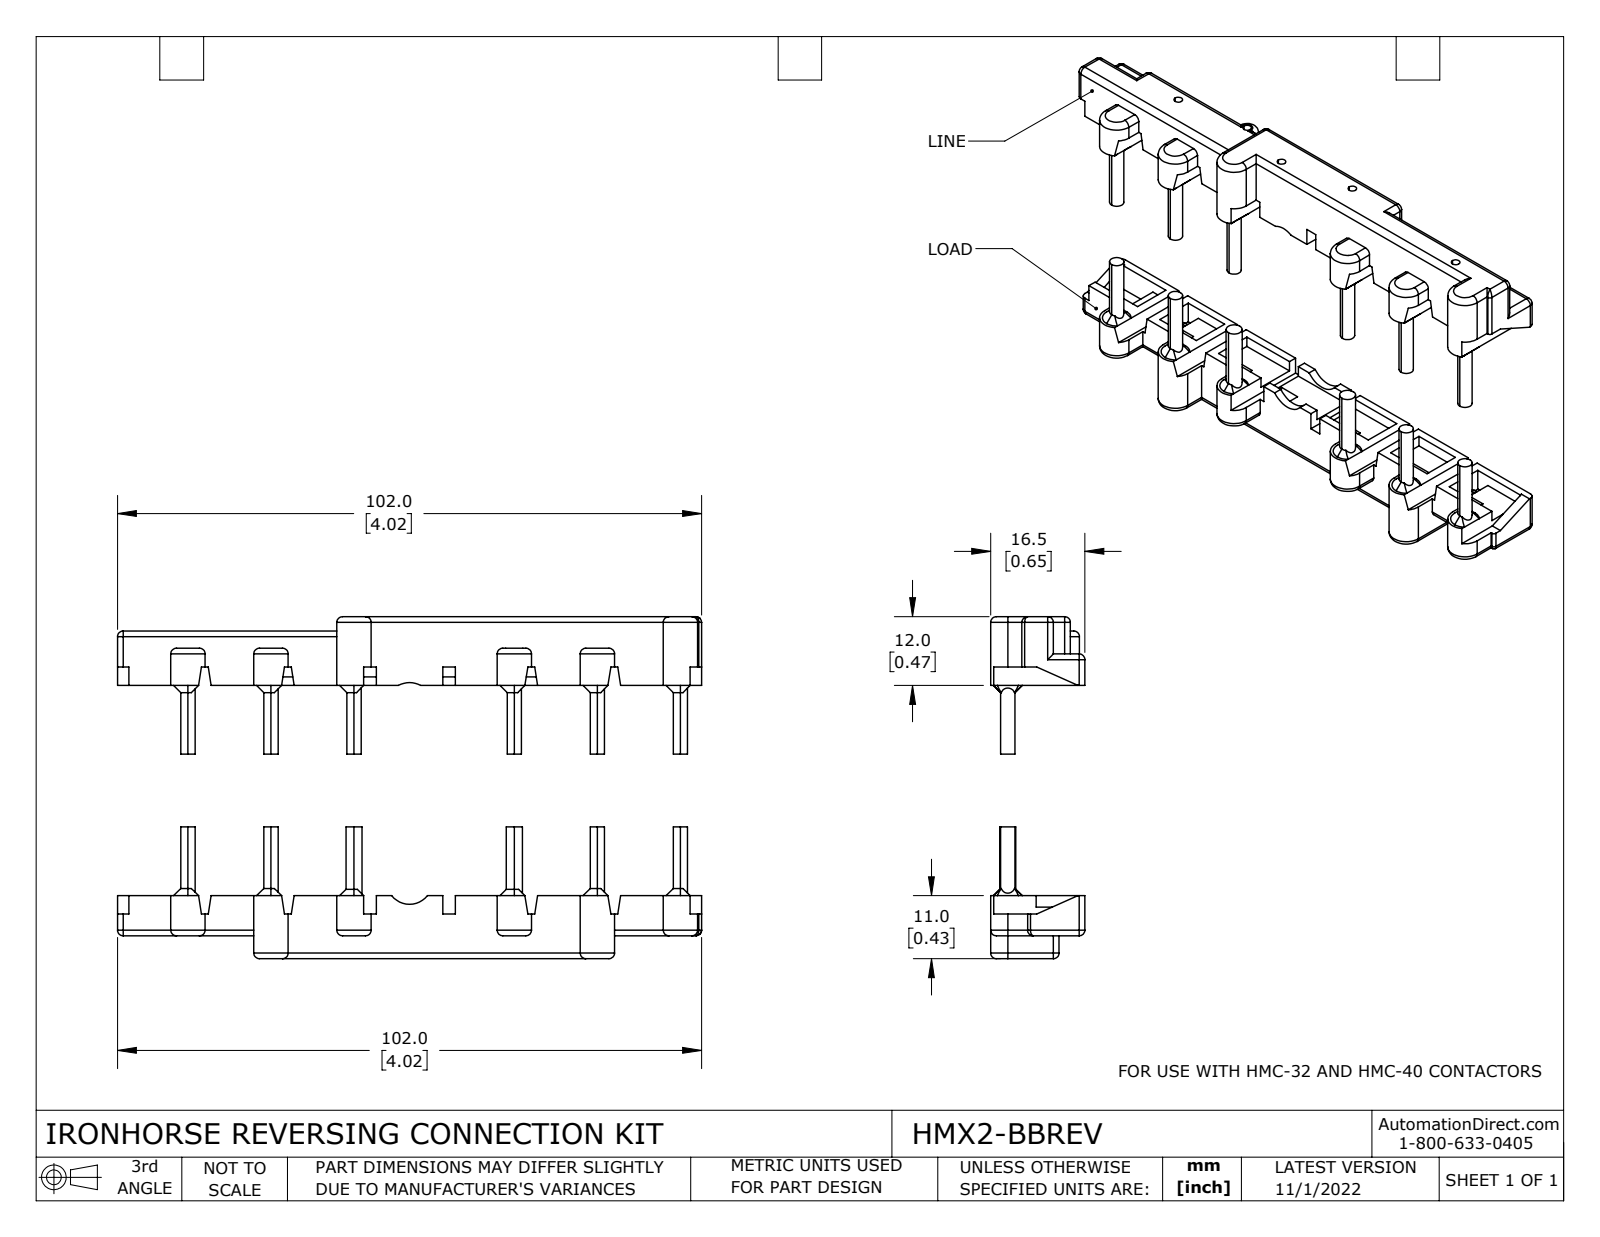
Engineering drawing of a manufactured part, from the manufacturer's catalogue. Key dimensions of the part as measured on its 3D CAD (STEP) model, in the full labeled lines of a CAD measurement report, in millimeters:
Part name (STEP PRODUCT): HMX2-BBREV
STEP written by: SolidWorks 2021 (CONFIG_CONTROL_DESIGN)
Units: millimetres
Bodies: 2 solids, 552 faces (308 planar, 165 cylindrical, 79 other)
Overall size (bounding box): 102 × 59.7 × 16.5
Volume: 18 520 mm³ · Surface area: 14 120 mm²
Round holes (diameter × count): ⌀1.5 ×12
Round bosses / shafts (diameter × count): ⌀2.5 ×6, ⌀2.8 ×2
Partial cylindrical surfaces — rounded edges, fillets, slot ends (radius × count): R1 ×54, R3 ×6, R1.2 ×5, R0.5 ×2, R4 ×2, R1.4 ×1, R2 ×1
Main face-to-face distances: 1.5, 4, 1, 5.5, 2.5, 11, 5, 9.5, 7, 3
Hole centre spacings: 4.3, 14.2, 15.1, 28.1, 28.7, 29.3, 42.5, 43
